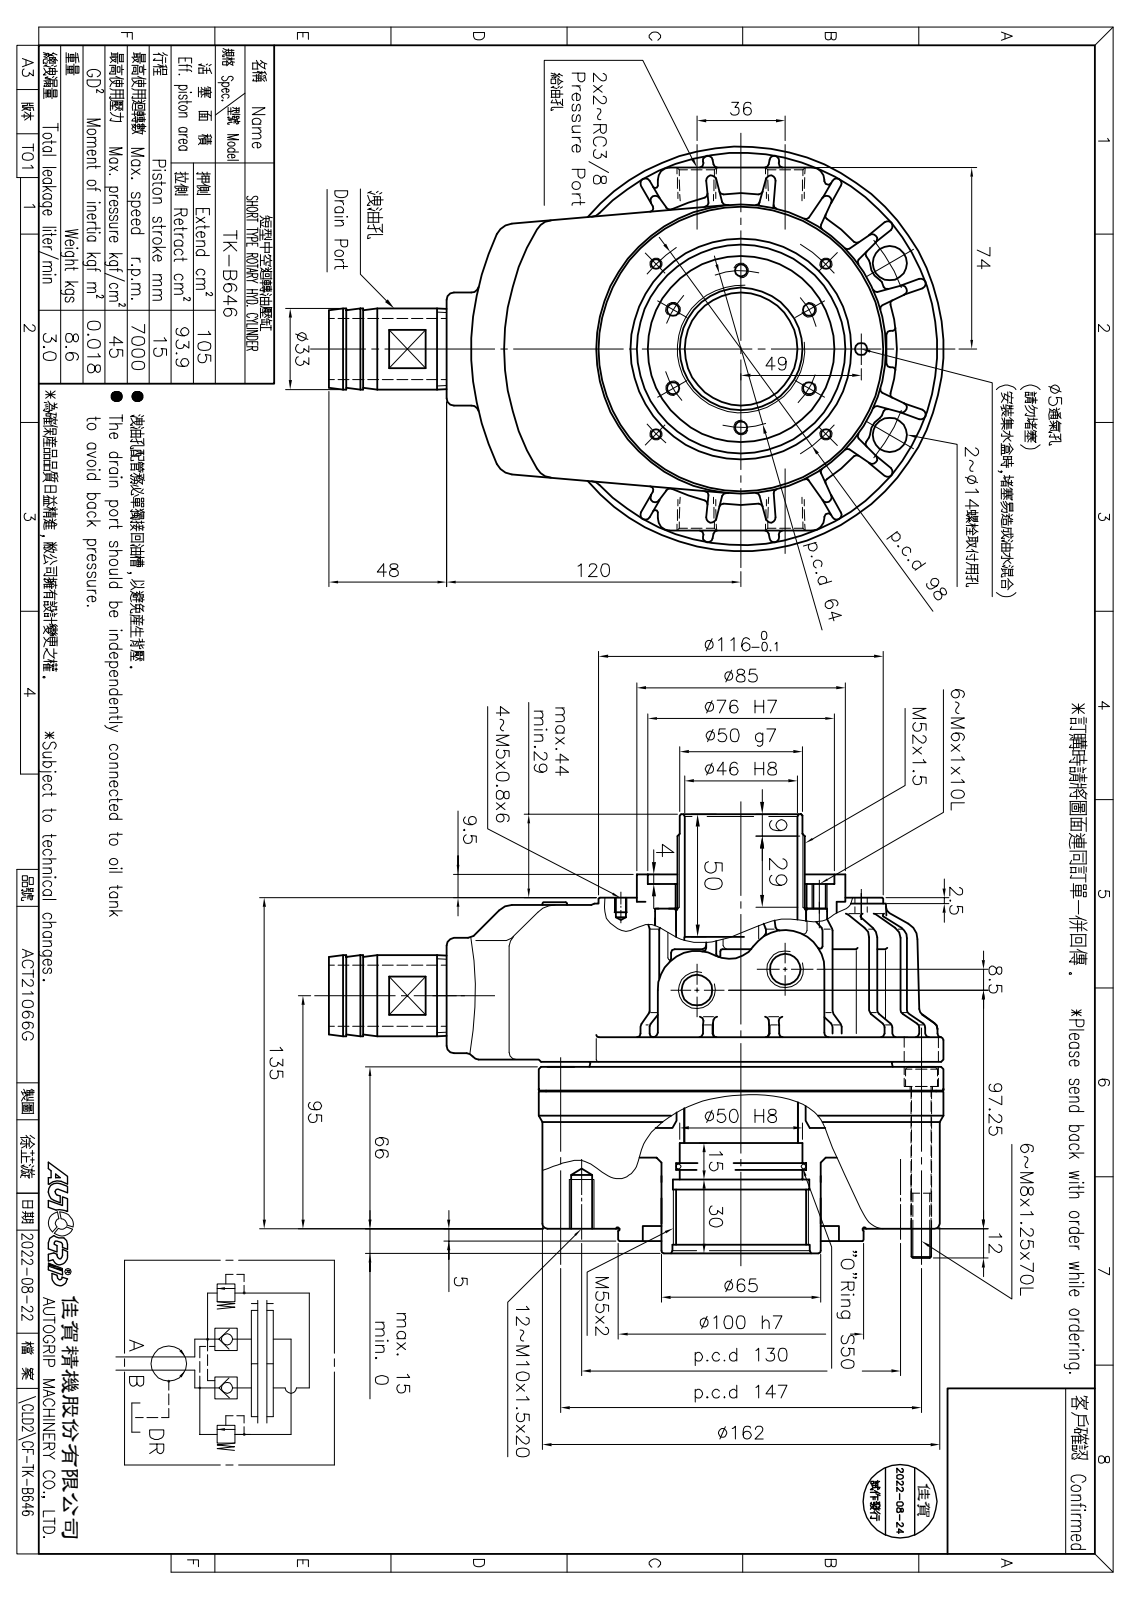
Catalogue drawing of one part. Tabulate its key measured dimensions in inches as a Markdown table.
| quantity | value |
| --- | --- |
| part name | CF-TK-646-08010; CT-S08-08000; O-RING_S50; 圓頭內六角螺栓_M8x70 (+3 more) |
| STEP written by | SolidWorks 2016 (CONFIG_CONTROL_DESIGN) |
| units | inches |
| bodies | 24 solids, 1284 faces (257 planar, 372 cylindrical, 655 other) |
| overall size | 9.862 × 7.047 × 6.496 |
| volume | 91.23 in³ |
| surface area | 651.6 in² |
| round holes (diameter × count) | 0.335 × 18, 0.354 × 18, 0.551 × 18, 0.268 × 14, 0.394 × 14, 0.315 × 12, 0.197 × 7, 0.161 × 4, 0.579 × 2, 0.984 × 1, 1.181 × 1, 1.811 × 1 |
| round bosses / shafts (diameter × count) | 0.512 × 6, 0.315 × 6, 6.496 × 1, 6.378 × 1, 4.882 × 1, 4.567 × 1, 3.937 × 1, 3.543 × 1 |
| partial cylindrical surfaces (radius × count) | 0.079 × 6, 0.197 × 6, 0.295 × 4, 0.118 × 2, 0.315 × 2, 0.63 × 2, 0.472 × 1, 0.925 × 1 |
| main face-to-face distances | 2.598, 0.591, 0.118, 0.039, 2.008, 2.677, 0.079, 0.394, 2.559, 2.638 |
| hole center spacings | 2.894, 5.012, 3.72, 5.699, 1.005, 1.98, 4.433, 1.005 |
